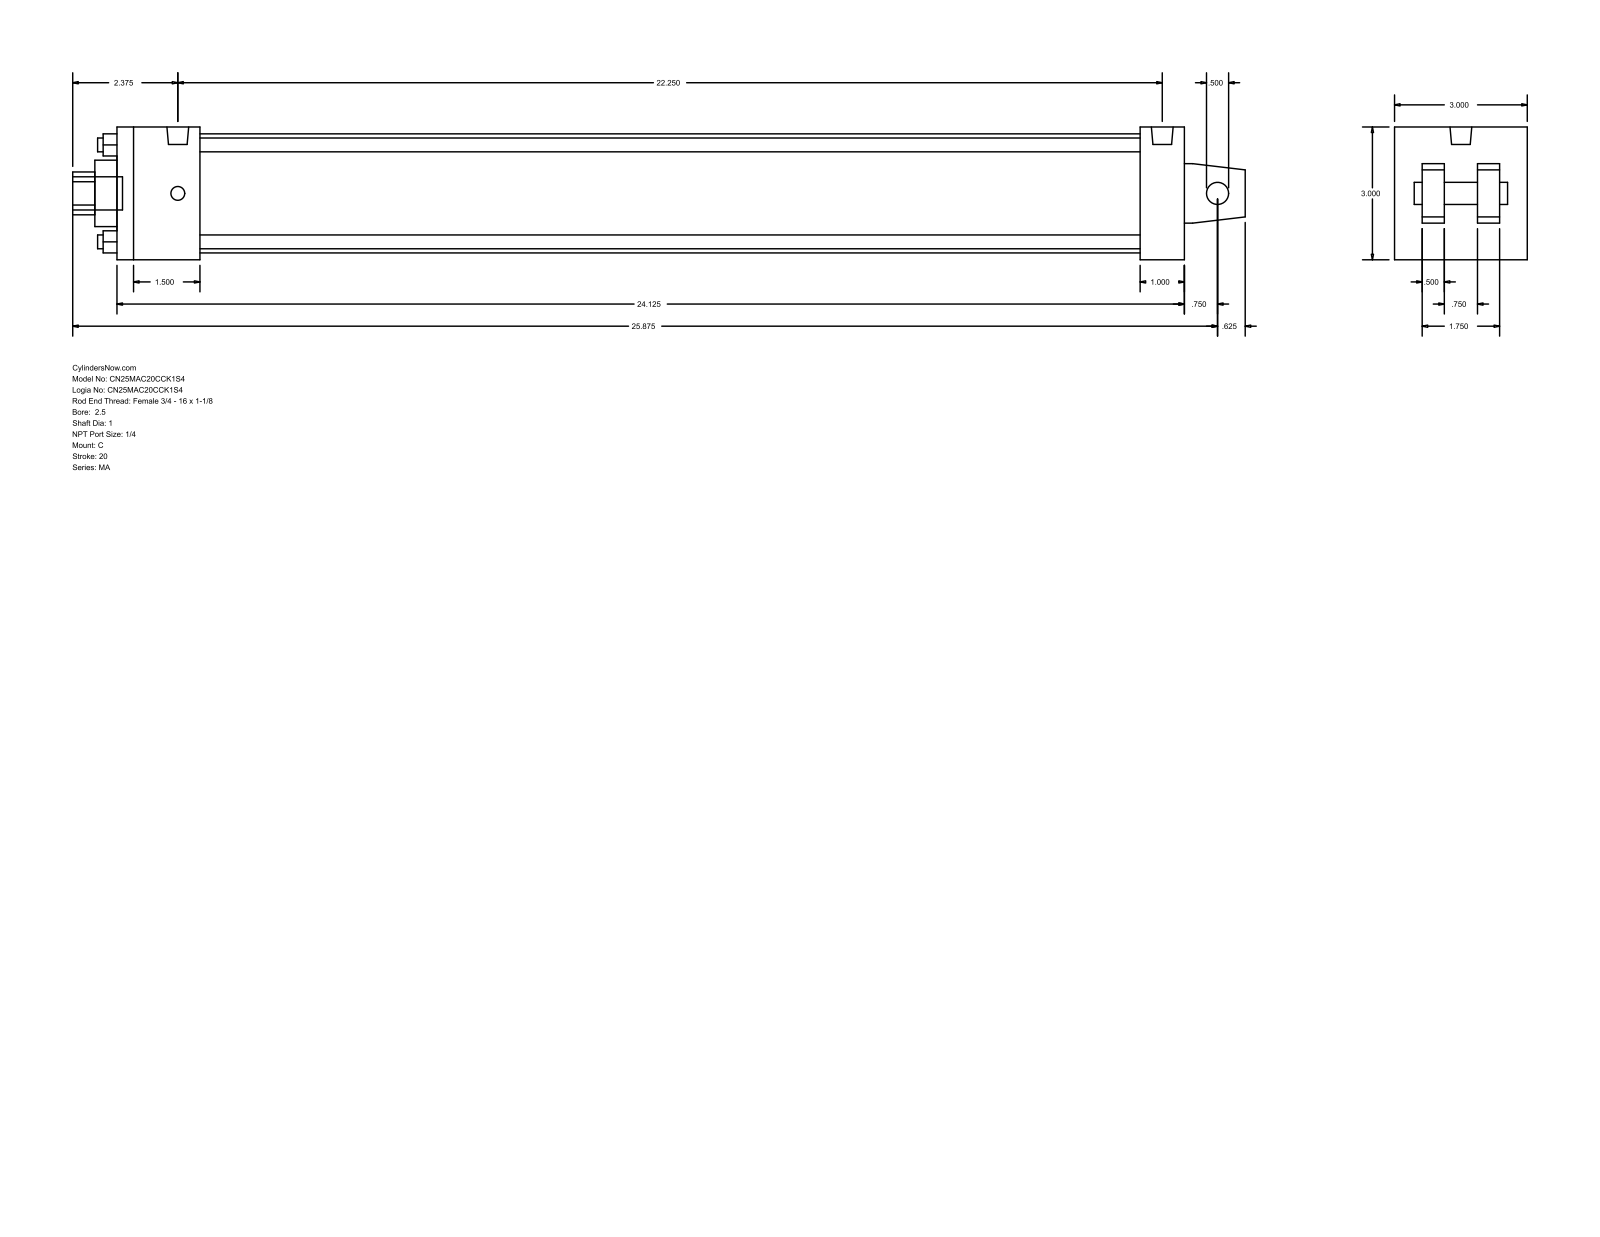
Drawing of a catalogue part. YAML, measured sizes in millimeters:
part_name: "MA_C__0250_1"
step_written_by: "GSSL Pune (CONFIG_CONTROL_DESIGN)"
units: millimeters
bodies: {solids: 0, faces: 103, planar: 76, cylindrical: 27, other: 0}
overall_size: [673.1, 76.2, 76.2]
round_holes:
  - {diameter: 7.94, count: 4}
  - {diameter: 12.7, count: 1}
  - {diameter: 25.4, count: 1}
  - {diameter: 38.1, count: 1}
  - {diameter: 68.33, count: 1}
round_bosses_or_shafts:
  - {diameter: 7.94, count: 4}
  - {diameter: 12.49, count: 2}
  - {diameter: 19.05, count: 1}
partial_cylinders:
  - {radius: 12.29, count: 1}
face_to_face_distances: [76.2, 612.77, 47.63, 12.7, 60.33, 15.87, 25.4, 28.57, 587.37, 539.74]
hole_center_spacings: [39.33, 55.62, 78.66]
